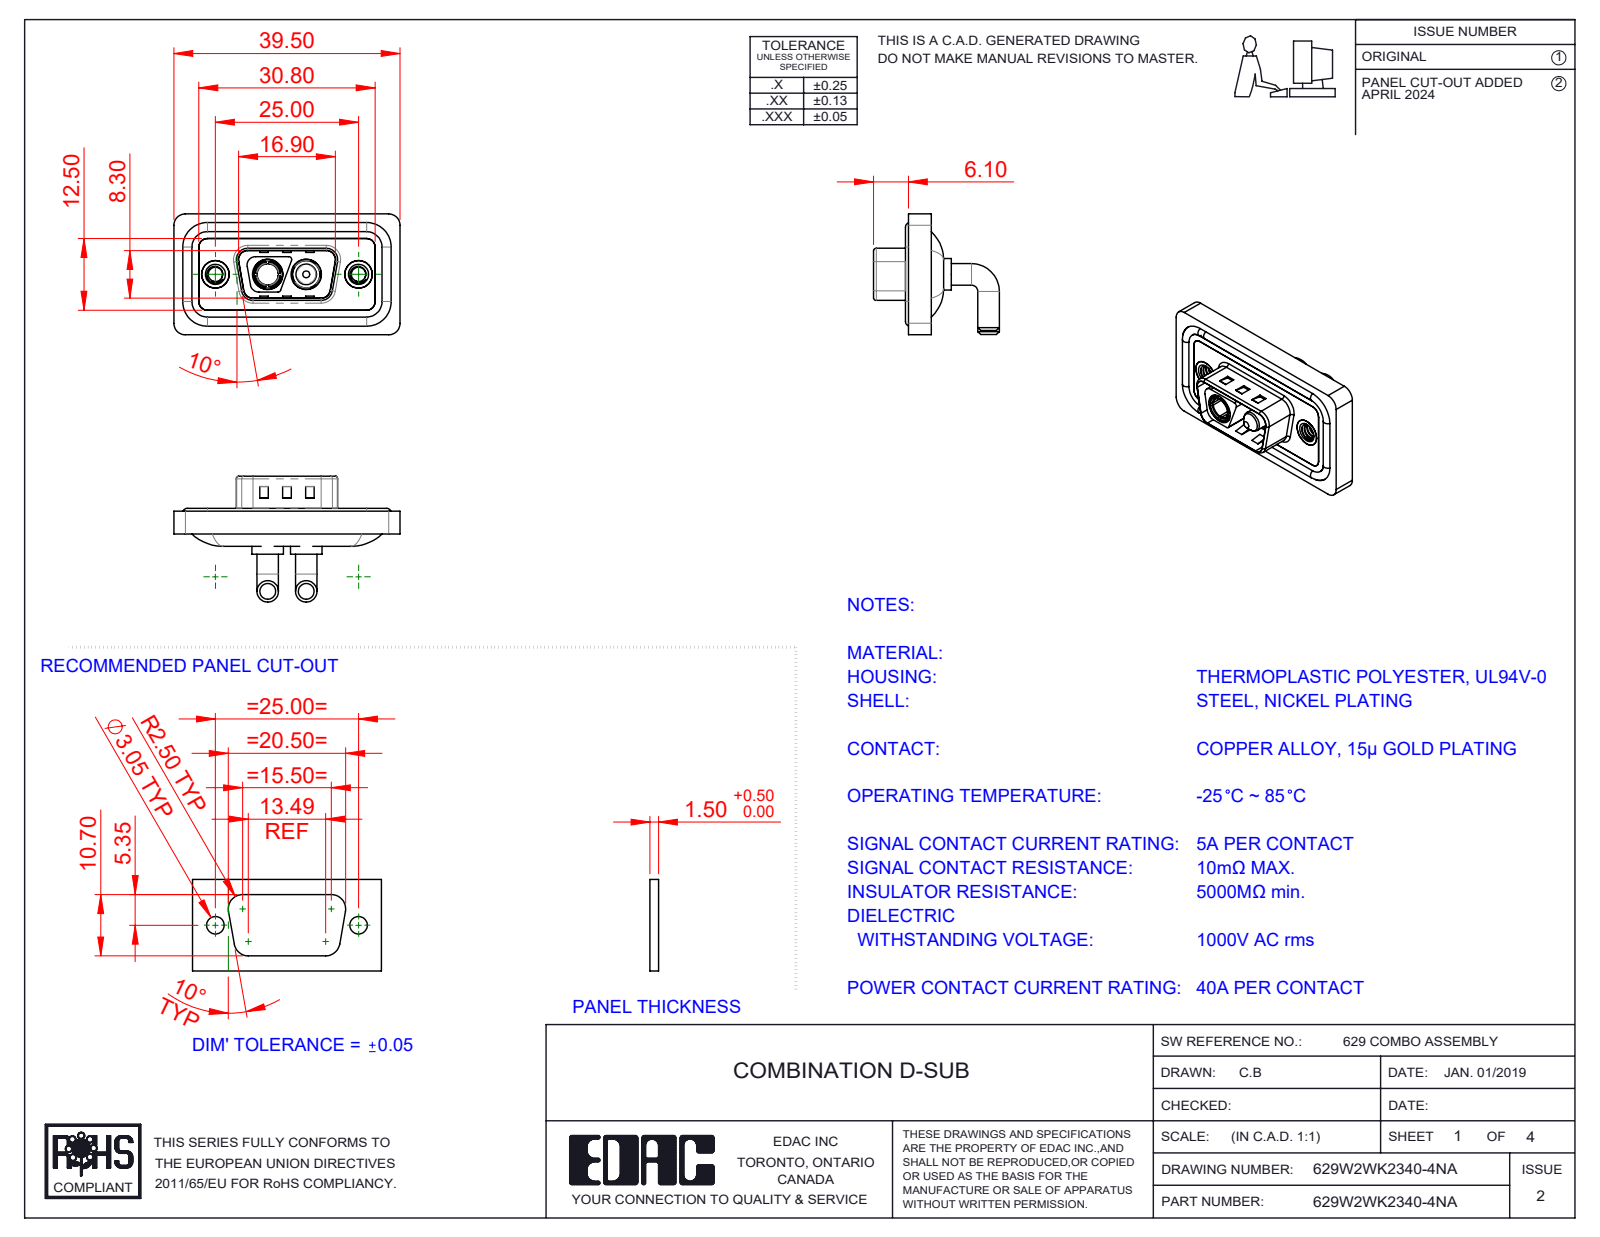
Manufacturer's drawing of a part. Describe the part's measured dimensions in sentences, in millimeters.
The part is named "629Combo Housing_2WK2; 629Combo Shell Rear_09 Contacts; 629W2WK2340-4NA; Power Socket_40A RA (+4 more)". Its 3-D file was written by "SolidWorks 2023 (CONFIG_CONTROL_DESIGN)". It is 11 solids with 536 faces: 189 planar, 229 cylindrical and 118 other. Overall it measures 39.5 by 21.98 by 21.1 millimeters. Its volume is 4 835 cubic millimeters and its surface area 7 625 square millimeters. Round holes: 2 of diameter 2.5, 2 of diameter 4, 2 of diameter 4.8, 2 of diameter 4.85, 2 of diameter 5, 2 of diameter 5.3, 1 of diameter 3.7. Round bosses or shafts: 4 of diameter 3.75, 4 of diameter 1.6, 2 of diameter 5.5, 2 of diameter 5.2, 2 of diameter 4.9, 2 of diameter 4.75, 1 of diameter 4.96, 1 of diameter 3.6. Partial cylindrical surfaces (rounded edges, fillets, slot ends): 20 of radius 1.5, 18 of radius 2, 10 of radius 0.5, 8 of radius 1.6, 4 of radius 0.25, 4 of radius 0.6, 4 of radius 0.65, 4 of radius 0.9. The main face-to-face distances are 0.4, 2.9, 1.1, 0.8, 2.1, 2.5, 3.1, 1.6, 4.5, 1.5. The hole center spacings are 9.14, 15.86, 6.72, 25.
